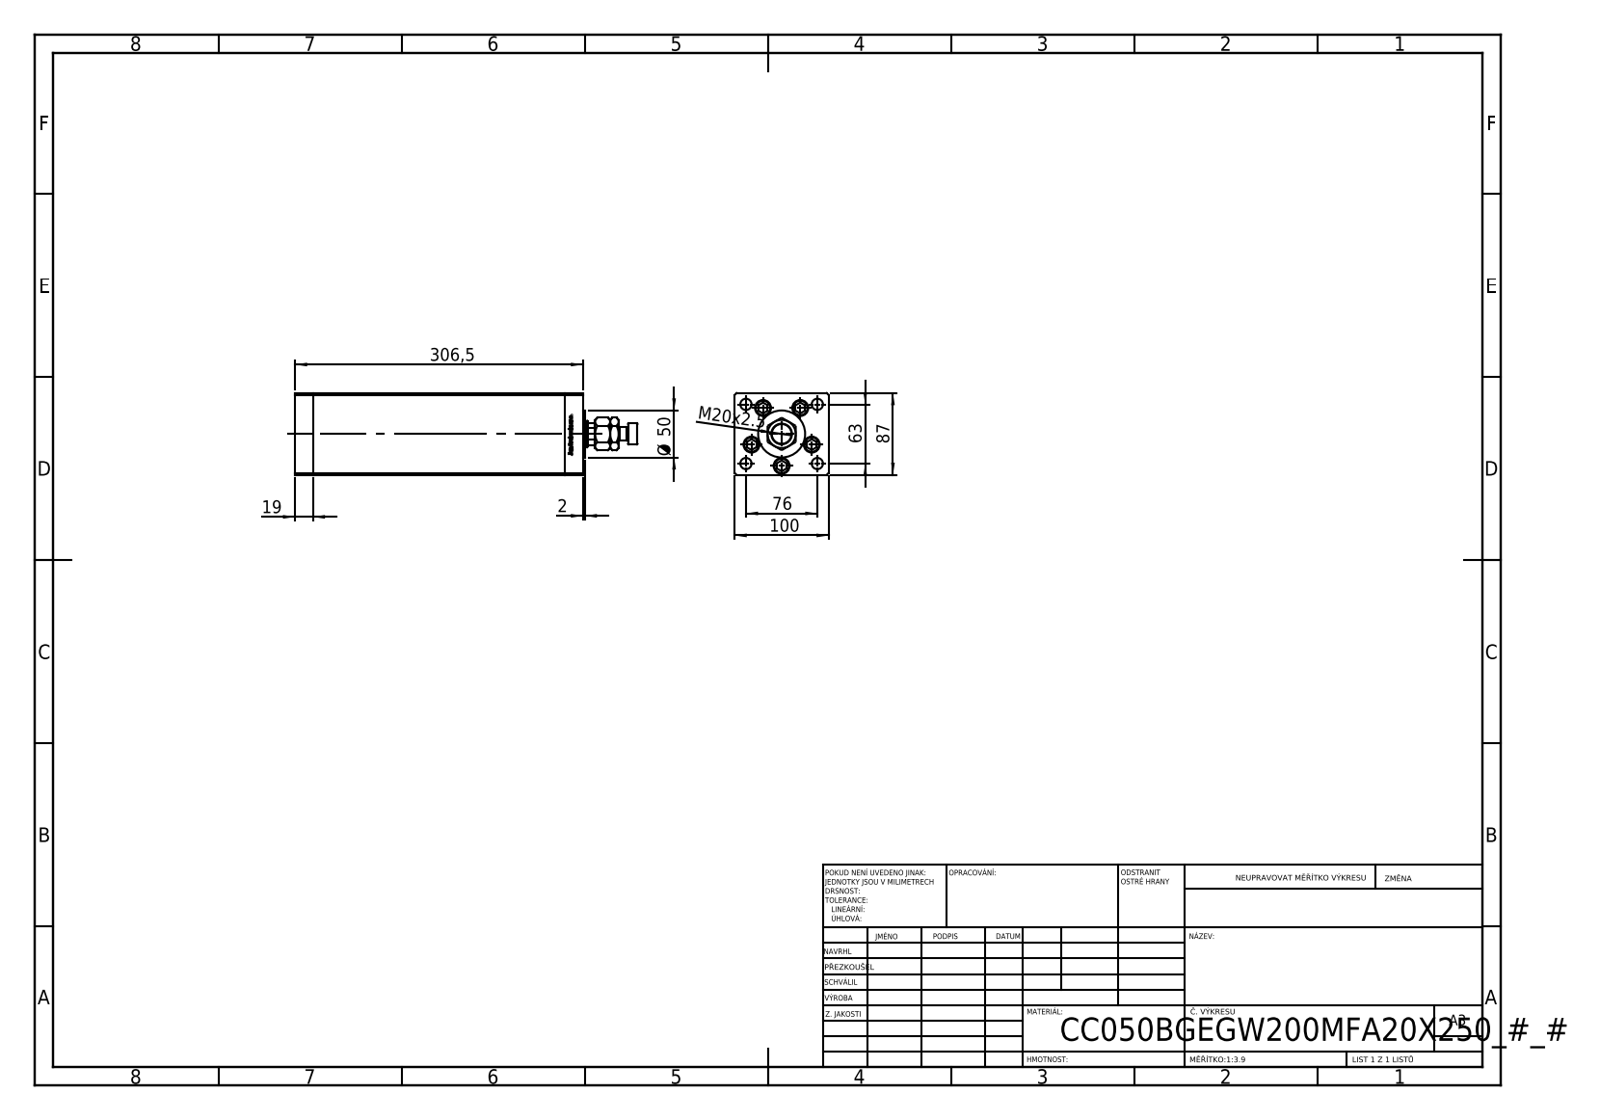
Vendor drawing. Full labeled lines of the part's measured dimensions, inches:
Part name (STEP PRODUCT): V220C_VC_B; MFA; ALLEN BOLT; V220C_B MIDDLE (+2 more)
STEP written by: SolidWorks 2019 (CONFIG_CONTROL_DESIGN)
Units: inches
Bodies: 15 solids, 1237 faces (480 planar, 151 cylindrical, 606 other)
Overall size (bounding box): 14.35 × 3.937 × 3.425
Volume: 141.3 in³ · Surface area: 445.7 in²
Round holes (diameter × count): ⌀0.531 ×7, ⌀0.669 ×5, ⌀0.472 ×4, ⌀0.079 ×2, ⌀0.518 ×2, ⌀0.728 ×1, ⌀1.102 ×1
Round bosses / shafts (diameter × count): ⌀0.315 ×5, ⌀0.669 ×2, ⌀1.969 ×1, ⌀0.866 ×1, ⌀0.551 ×1
Partial cylindrical surfaces — rounded edges, fillets, slot ends (radius × count): R0.037 ×2, R0.531 ×1
Main face-to-face distances: 3.937, 3.425, 0.748, 10.571, 11.319, 1.348, 12.067, 0.6, 9.97, 10.719
Hole centre spacings: 1.339, 0.732, 1.561, 1.943, 2.281, 0.828, 1.499, 1.546
